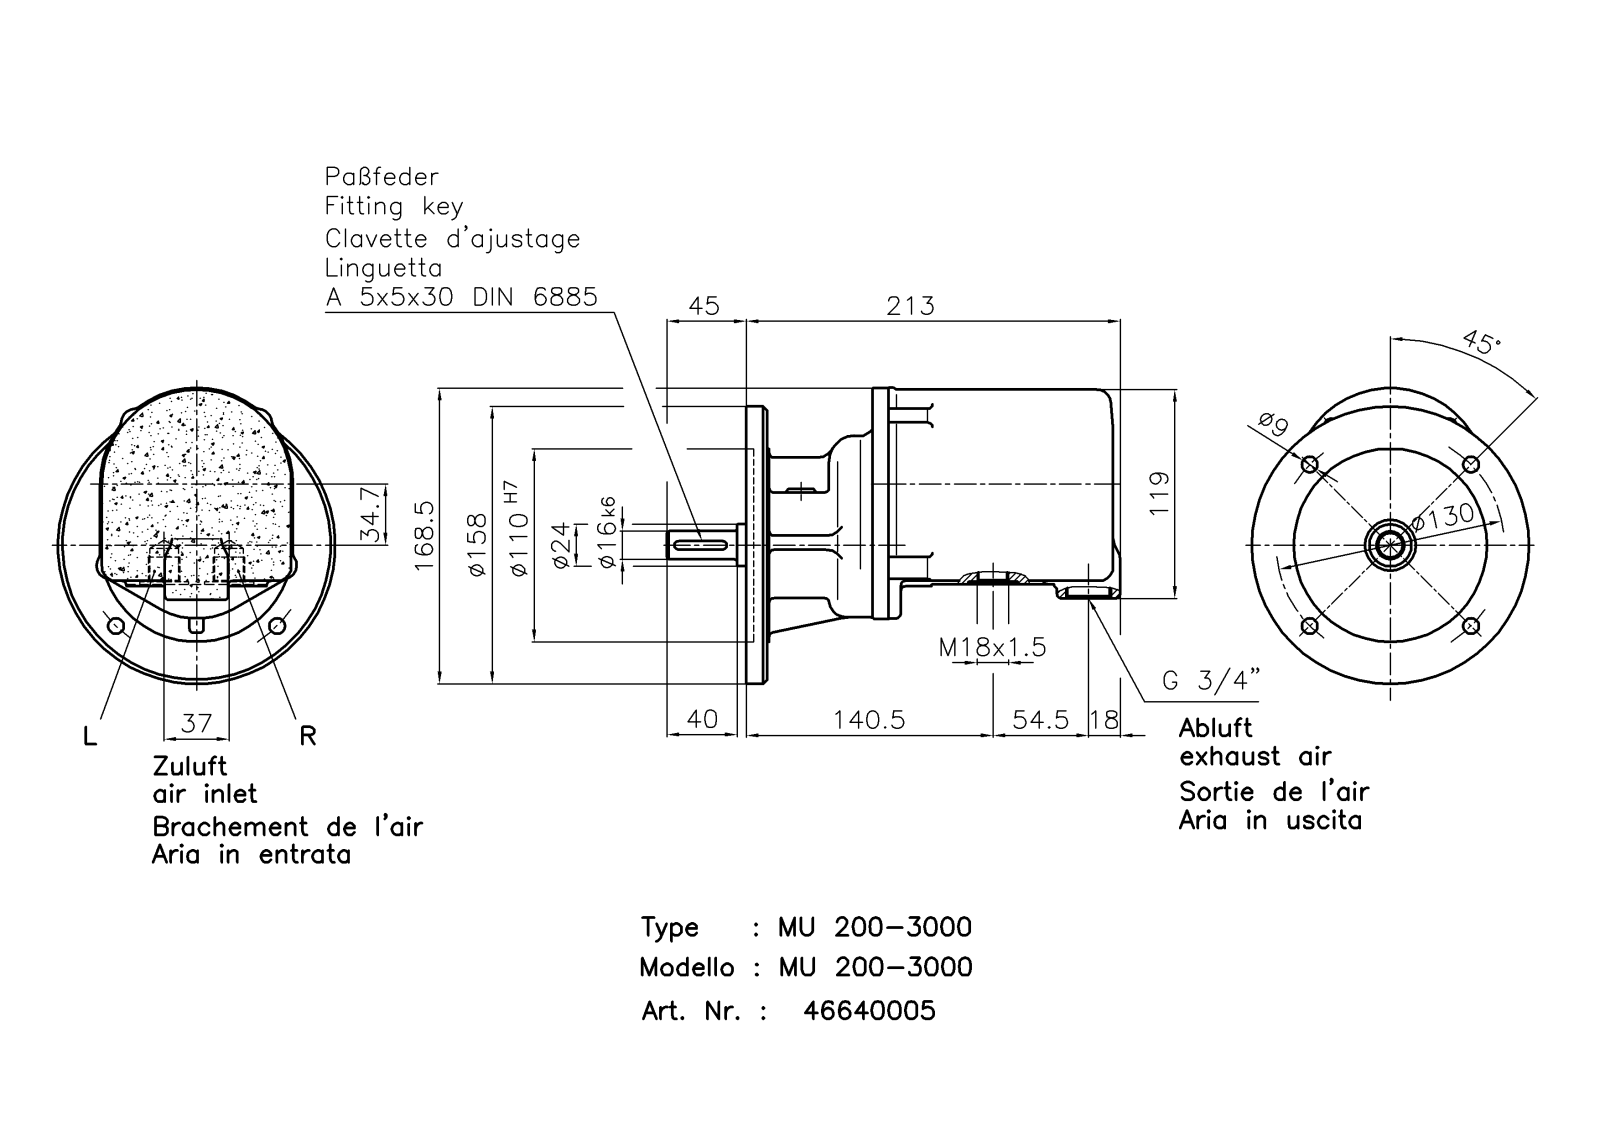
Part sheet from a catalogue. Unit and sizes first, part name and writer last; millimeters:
Units: millimetres
Overall size (bounding box): 258.2 × 168.5 × 158
Round holes (diameter × count): ⌀6.4 ×5, ⌀20 ×2, ⌀4 ×1, ⌀38.2 ×1, ⌀40 ×1, ⌀72 ×1
Round bosses / shafts (diameter × count): ⌀11 ×5, ⌀10 ×5, ⌀6 ×5, ⌀158 ×1, ⌀110 ×1, ⌀97.97 ×1, ⌀82 ×1, ⌀46.65 ×1
Partial cylindrical surfaces — rounded edges, fillets, slot ends (radius × count): R2.5 ×43, R2 ×42, R8 ×14, R10 ×5, R1 ×2, R1.13 ×2, R3.95 ×2, R4 ×2
Main face-to-face distances: 4, 104, 12, 1, 13, 59, 108, 72, 60, 100
Hole centre spacings: 48.51, 52.89, 76.39, 81.49, 110.05, 114.11, 36.25, 67.88
Volume: 1 767 000 mm³ · Surface area: 231 804 mm²
Bodies: 1 solid, 697 faces (256 planar, 209 cylindrical, 232 other)
Part name (STEP PRODUCT): MU 200-1400_46600005
STEP written by: Autodesk Inventor 2008 (CONFIG_CONTROL_DESIGN)
